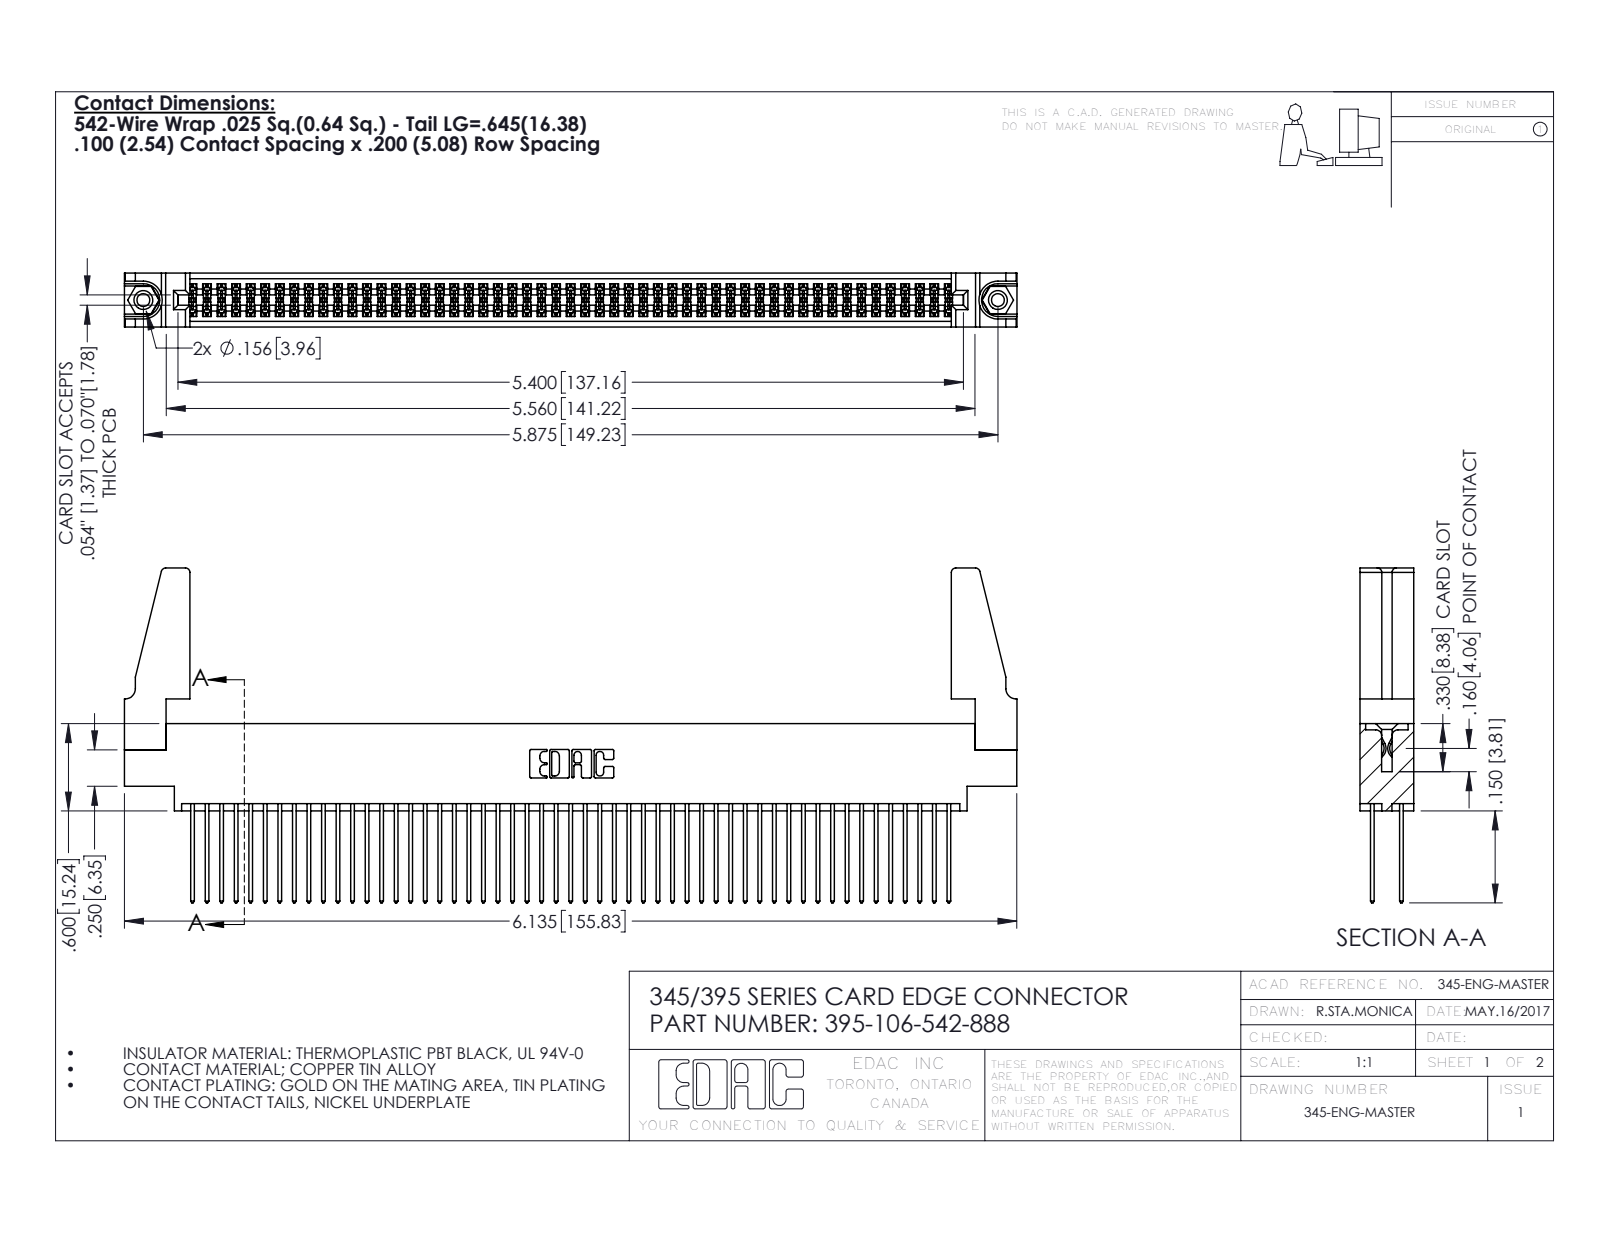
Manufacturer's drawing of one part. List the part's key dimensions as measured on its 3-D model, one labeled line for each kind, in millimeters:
Part name (STEP PRODUCT): 345 Part_0.170 Offset - 0.156 Dia-TH; 345-220-078_345-220-088; 395-106-542-888; 345-250-001_345-250-001-102 (+1 more)
STEP written by: SolidWorks 2016 (CONFIG_CONTROL_DESIGN)
Units: millimetres
Bodies: 111 solids, 5554 faces (3654 planar, 1884 cylindrical, 16 other)
Overall size (bounding box): 155.9 × 58.5 × 9.4
Volume: 18 880 mm³ · Surface area: 28 880 mm²
Round holes (diameter × count): ⌀2.3 ×2, ⌀3.2 ×2, ⌀4 ×2, ⌀1.6 ×1
Round bosses / shafts (diameter × count): ⌀3.9 ×2
Partial cylindrical surfaces — rounded edges, fillets, slot ends (radius × count): R0.2 ×159, R0.3 ×106, R0.3 ×22, R0.8 ×8, R0.2 ×6, R0.8 ×6, R0.7 ×3, R0.4 ×2
Main face-to-face distances: 1.8, 7.6, 5.1, 2.5, 6.9, 0.6, 9.4, 5.7, 4.4, 3.8
Hole centre spacings: 6.9, 143.2, 149.2
